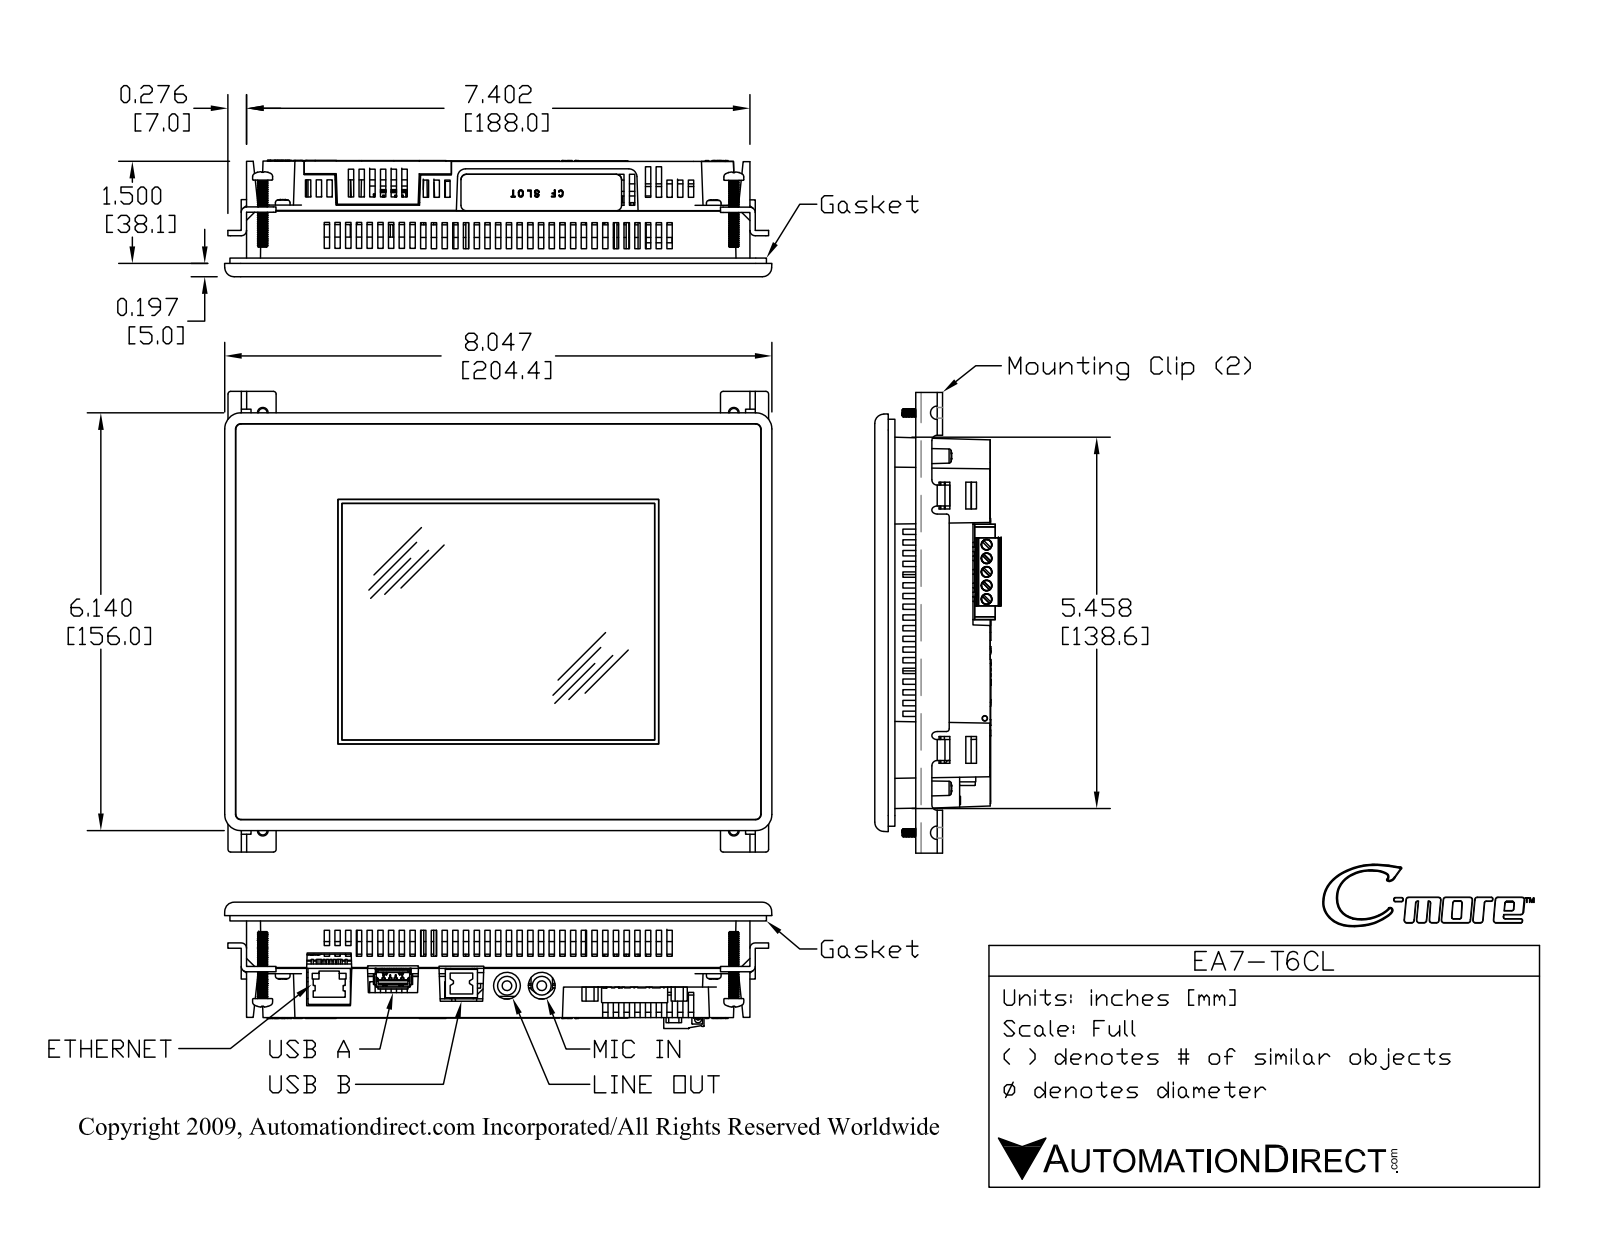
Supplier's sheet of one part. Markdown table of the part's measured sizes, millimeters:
| quantity | value |
| --- | --- |
| part name | EA7-T6CL |
| STEP written by | SolidWorks 2009 (AUTOMOTIVE_DESIGN) |
| units | millimeters |
| bodies | 1 solid, 483 faces (370 planar, 95 cylindrical, 18 other) |
| overall size | 204.4 × 156 × 47.15 |
| volume | 307 532 mm³ |
| surface area | 201 007 mm² |
| round holes (diameter × count) | 3.5 × 3, 9.65 × 2, 4.5 × 1 |
| round bosses / shafts (diameter × count) | 8 × 1, 6.5 × 1 |
| partial cylindrical surfaces (radius × count) | 2 × 20, 1 × 16, 3.08 × 5, 3.58 × 5, 2.5 × 4, 3.98 × 4, 4 × 4, 6 × 4 |
| main face-to-face distances | 3.04, 1.96, 41.14, 43.1, 38.1, 40.06, 135.56, 174.46, 138.6, 34.2 |
| hole center spacings | 12.8, 30.35 |
